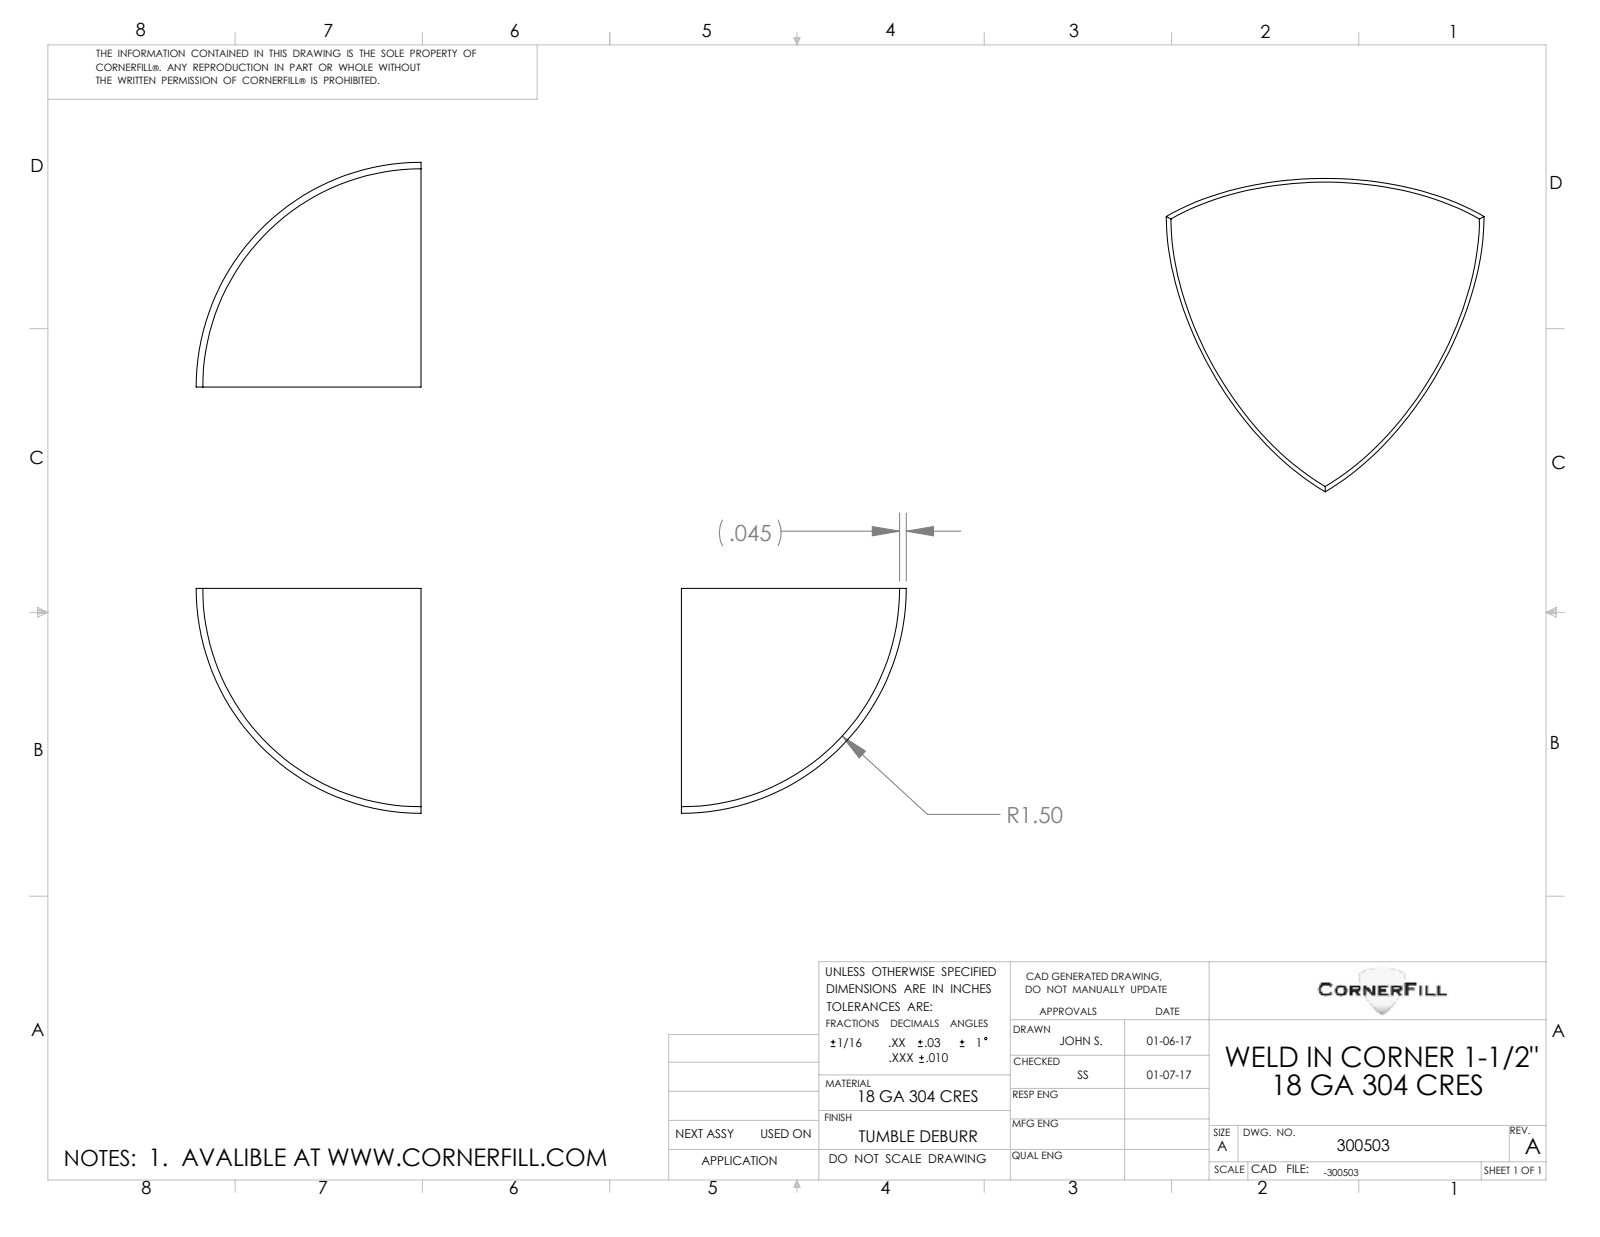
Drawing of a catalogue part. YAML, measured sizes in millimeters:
part_name: "300503"
step_written_by: "SolidWorks 2016 (CONFIG_CONTROL_DESIGN)"
units: millimeters
bodies: {solids: 1, faces: 5, planar: 3, cylindrical: 0, other: 2}
overall_size: [39.2, 39.2, 39.2]
volume: 2690
surface_area: 4908
